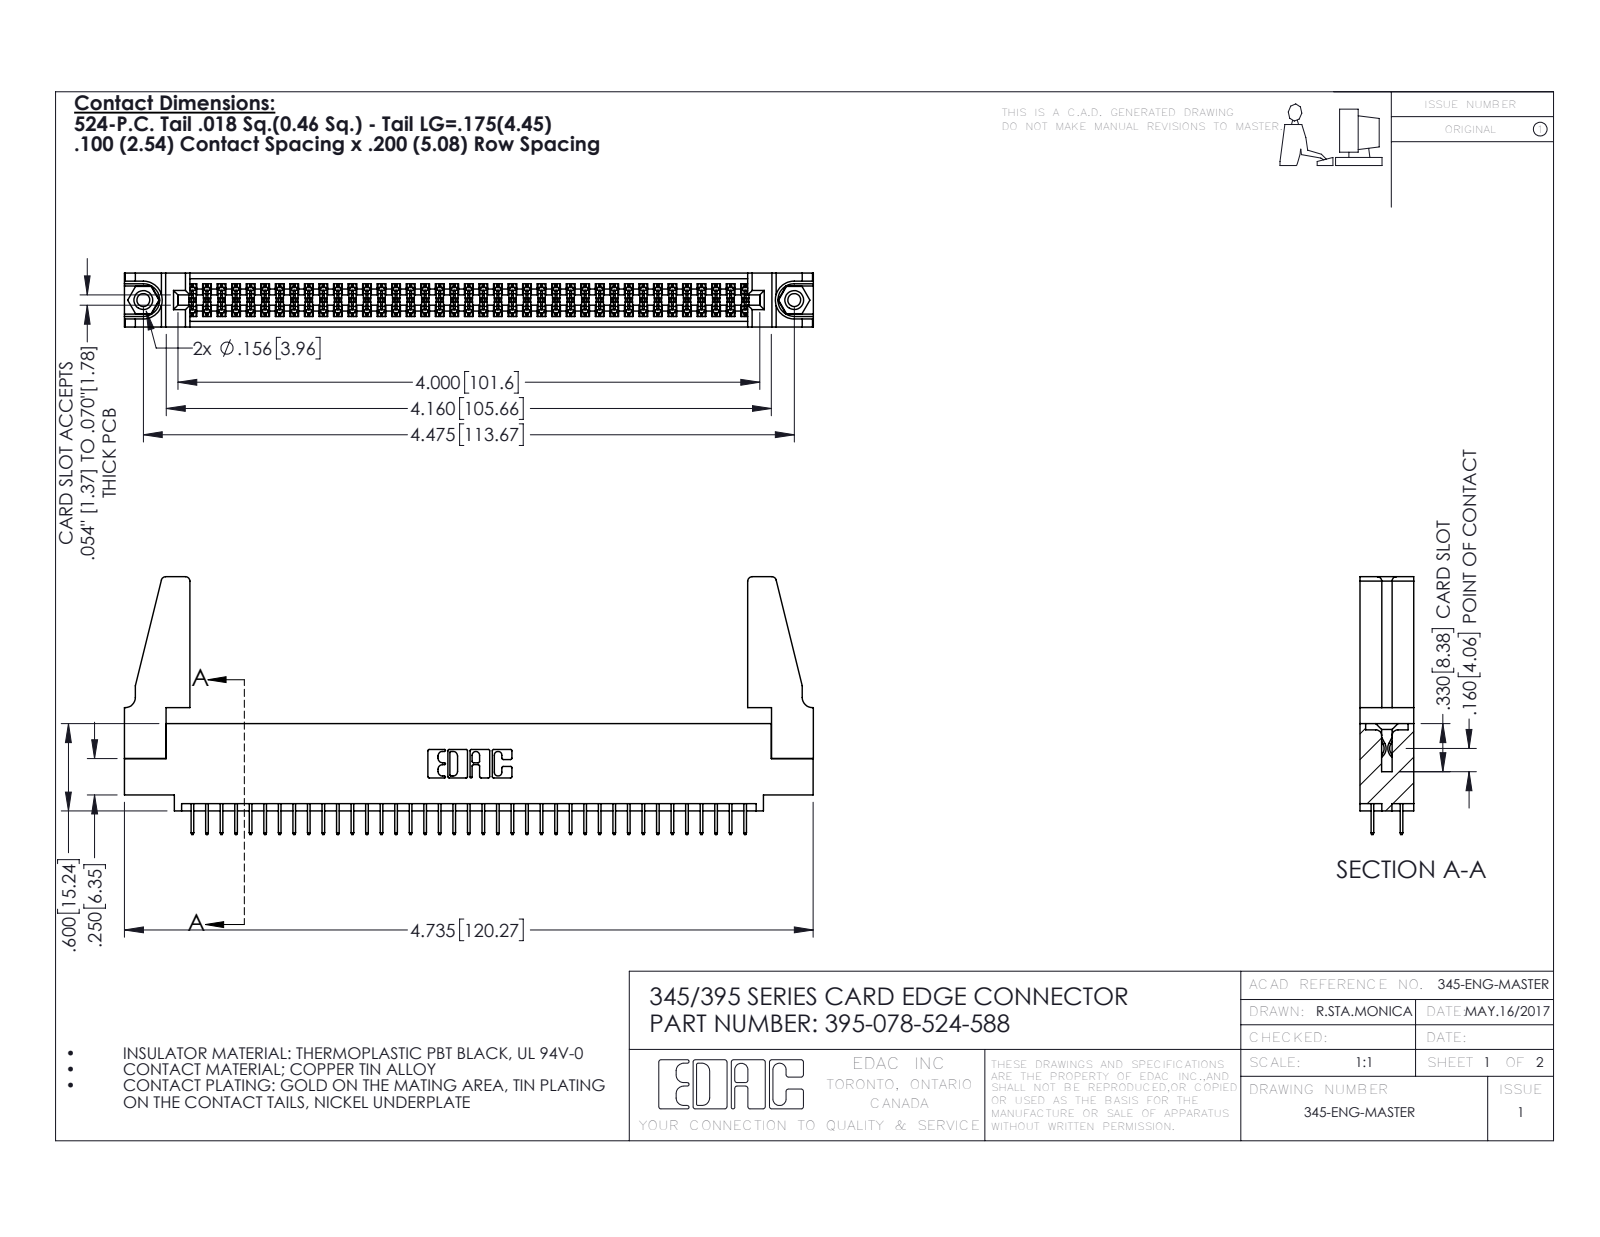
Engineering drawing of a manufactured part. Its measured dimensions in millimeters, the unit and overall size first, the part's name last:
Units: millimetres
Overall size (bounding box): 120.3 × 45 × 9.4
Round holes (diameter × count): ⌀2.3 ×2, ⌀3.2 ×2, ⌀4 ×2, ⌀1.6 ×1
Round bosses / shafts (diameter × count): ⌀3.9 ×2
Partial cylindrical surfaces — rounded edges, fillets, slot ends (radius × count): R0.2 ×117, R0.3 ×22, R0.8 ×8, R0.2 ×6, R0.8 ×6, R0.7 ×3, R0.4 ×2, R0.5 ×2
Main face-to-face distances: 1.8, 7.6, 9.4, 5.1, 2.5, 6.9, 0.6, 5.7, 1.8, 4.4
Hole centre spacings: 6.9, 107.7, 113.7
Volume: 14 700 mm³ · Surface area: 19 790 mm²
Bodies: 83 solids, 4466 faces (3198 planar, 1252 cylindrical, 16 other)
Part name (STEP PRODUCT): 345-250-001_345-250-001-102; 345 Part_0.110 Offset - 0.156 Dia-TH; 345-292-001_345-293-124; 345-220-078_345-220-088 (+1 more)
STEP written by: SolidWorks 2016 (CONFIG_CONTROL_DESIGN)
